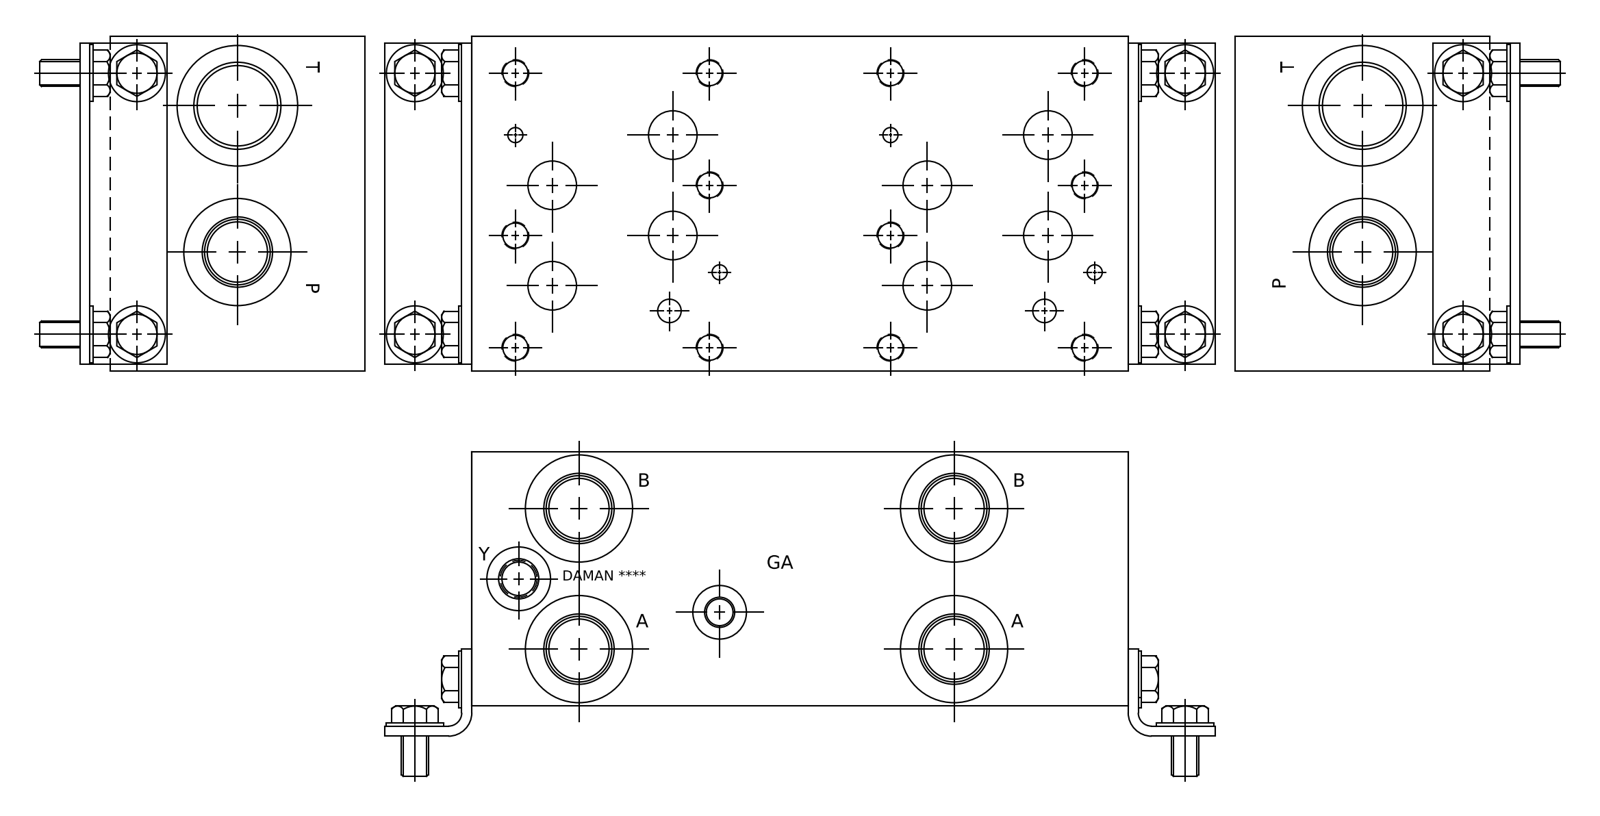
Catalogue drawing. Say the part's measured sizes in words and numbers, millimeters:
The part is named "Part_DD08P027S_3D". Its 3-D file was written by "Autodesk Inventor 2019 (AUTOMOTIVE_DESIGN)". It is 1 solid with 694 faces: 364 planar, 100 cylindrical and 230 other. Overall it measures 311.15 by 158.75 by 120.65 millimeters. Its volume is 5 573 000 cubic millimeters and its surface area 273 105 square millimeters. Round holes: 15 of diameter 10.72, 14 of diameter 12.7, 7 of diameter 23.01, 5 of diameter 31.27, 5 of diameter 33.76, 5 of diameter 49.12, 4 of diameter 7.14, 4 of diameter 28.57, 4 of diameter 33.35, 4 of diameter 35.51, 2 of diameter 33.34, 1 of diameter 11.11. The main face-to-face distances are 120.65, 158.75, 311.15, 0.79, 157.96, 310.36, 309.57, 19.84, 19.05, 291.31. The hole center spacings are 177.8, 29.53, 29.54, 47.62, 61.92, 74.63, 184.07, 53.18.
